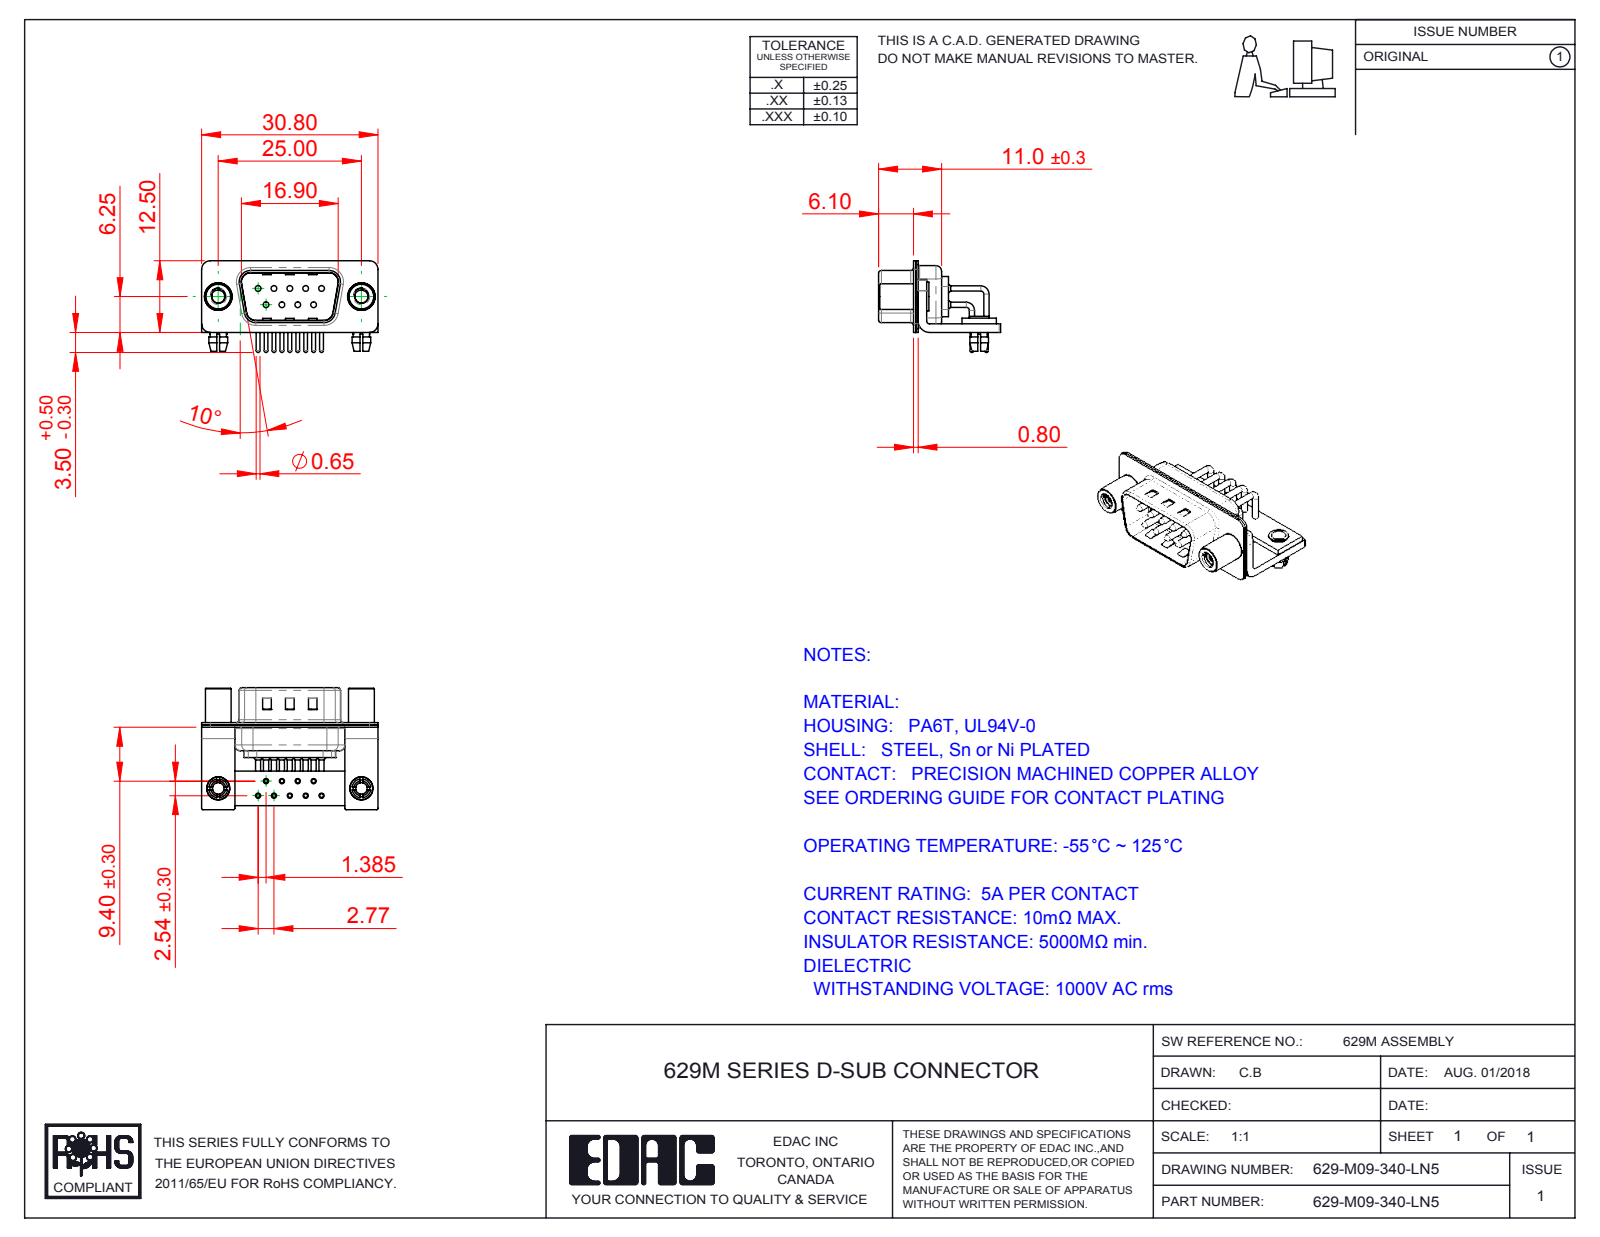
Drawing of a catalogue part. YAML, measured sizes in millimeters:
part_name: "629-M09-340-LN5; 629M Board Lock; 629M Stabilizer Bracket; 629M Contact Row 2 (+6 more)"
step_written_by: "SolidWorks 2016 (CONFIG_CONTROL_DESIGN)"
units: millimeters
bodies: {solids: 19, faces: 1504, planar: 759, cylindrical: 567, other: 178}
overall_size: [30.8, 21.3, 16]
volume: 1984
surface_area: 5510
round_holes:
  - {diameter: 2, count: 11}
  - {diameter: 0.9, count: 9}
  - {diameter: 1, count: 9}
  - {diameter: 1.7, count: 9}
  - {diameter: 2.26, count: 2}
  - {diameter: 2.5, count: 2}
  - {diameter: 3.2, count: 2}
  - {diameter: 4, count: 2}
  - {diameter: 4.8, count: 2}
round_bosses_or_shafts:
  - {diameter: 1.5, count: 9}
  - {diameter: 0.9, count: 9}
  - {diameter: 0.65, count: 9}
  - {diameter: 5, count: 2}
  - {diameter: 4.9, count: 2}
  - {diameter: 4.5, count: 2}
  - {diameter: 4, count: 2}
  - {diameter: 3.4, count: 2}
partial_cylinders:
  - {radius: 0.25, count: 16}
  - {radius: 1.5, count: 16}
  - {radius: 2, count: 13}
  - {radius: 0.5, count: 9}
  - {radius: 1.01, count: 9}
  - {radius: 1.6, count: 8}
  - {radius: 0.6, count: 4}
  - {radius: 0.65, count: 4}
face_to_face_distances: [0.4, 1.5, 0.8, 0.85, 1.25, 1.9, 1, 2.5, 10.4, 9.55]
hole_center_spacings: [2.77, 5.54, 3.16, 4.87, 8.31, 2.89, 2.9, 5.03]
